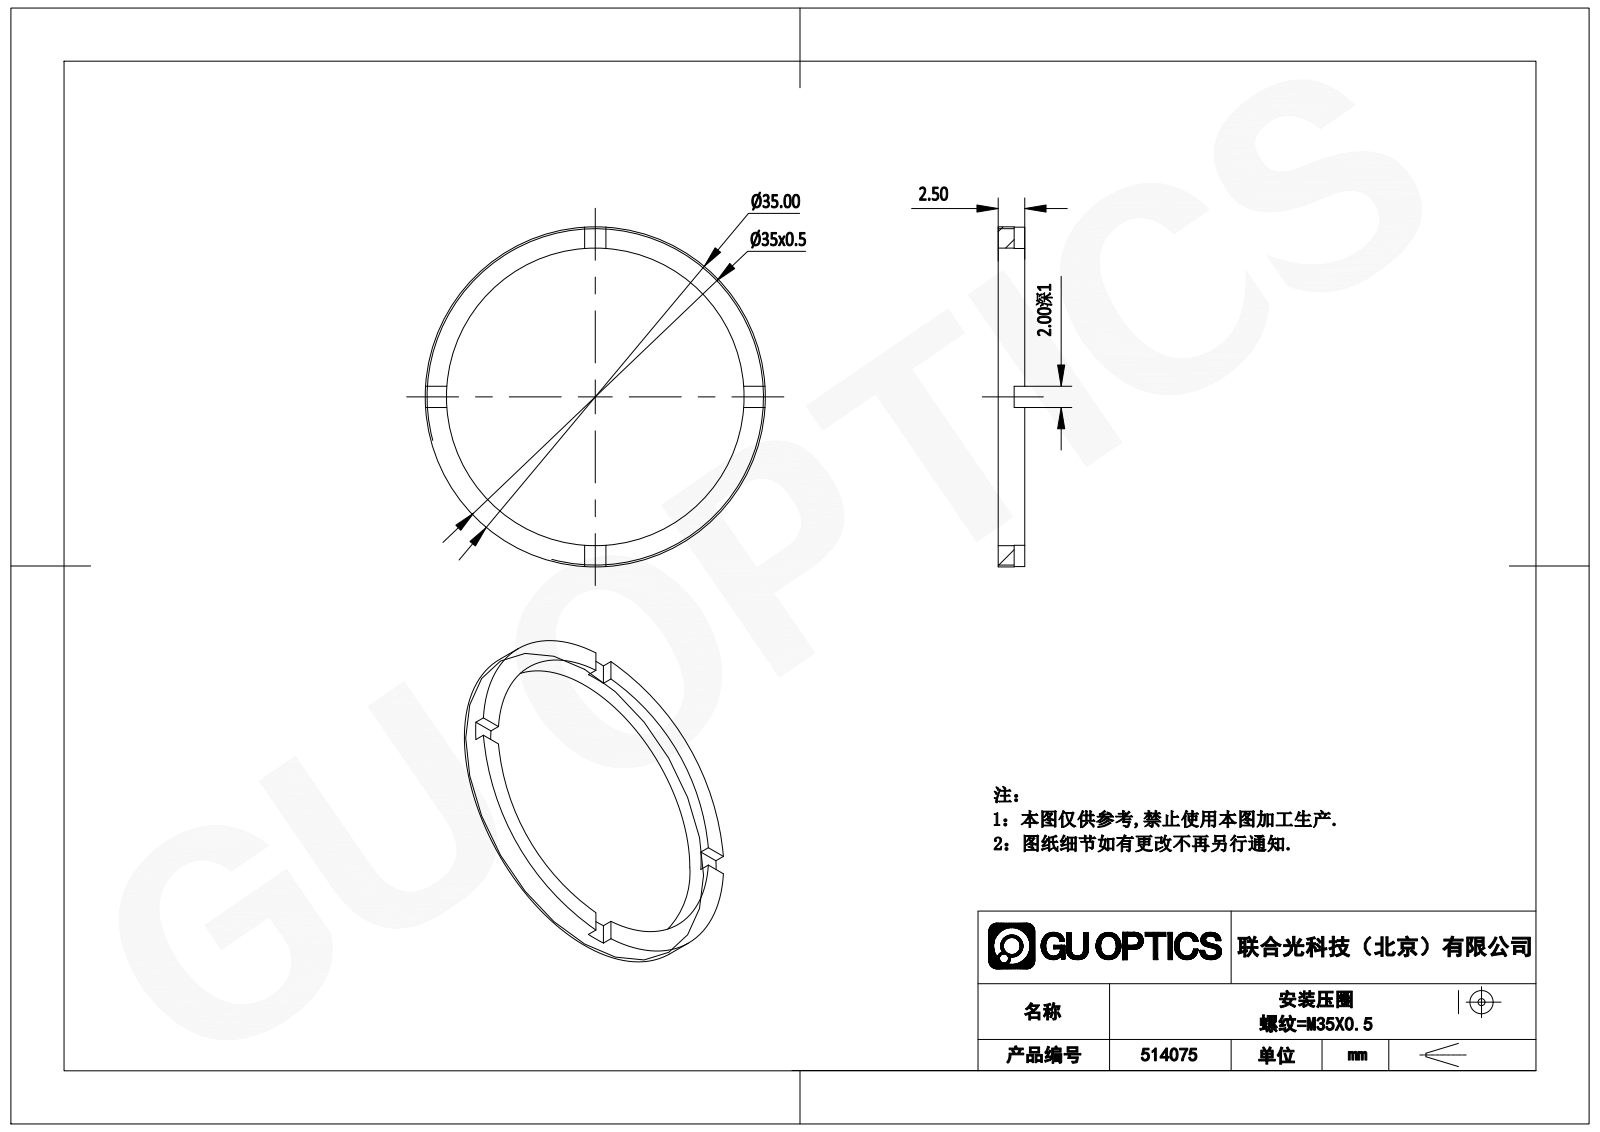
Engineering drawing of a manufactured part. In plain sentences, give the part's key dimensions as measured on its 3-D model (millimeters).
The part is named "514075". Its 3-D file was written by "SolidWorks 2020 (CONFIG_CONTROL_DESIGN)". It is 1 solid with 21 faces: 17 planar, 4 cylindrical and 0 other. Overall it measures 35 by 35 by 2.5 millimeters. Its volume is 502 cubic millimeters and its surface area 933 square millimeters. Round holes: 1 of diameter 31. Round bosses or shafts: 1 of diameter 35. The main face-to-face distances are 2.5, 1.5, 1, 2.
